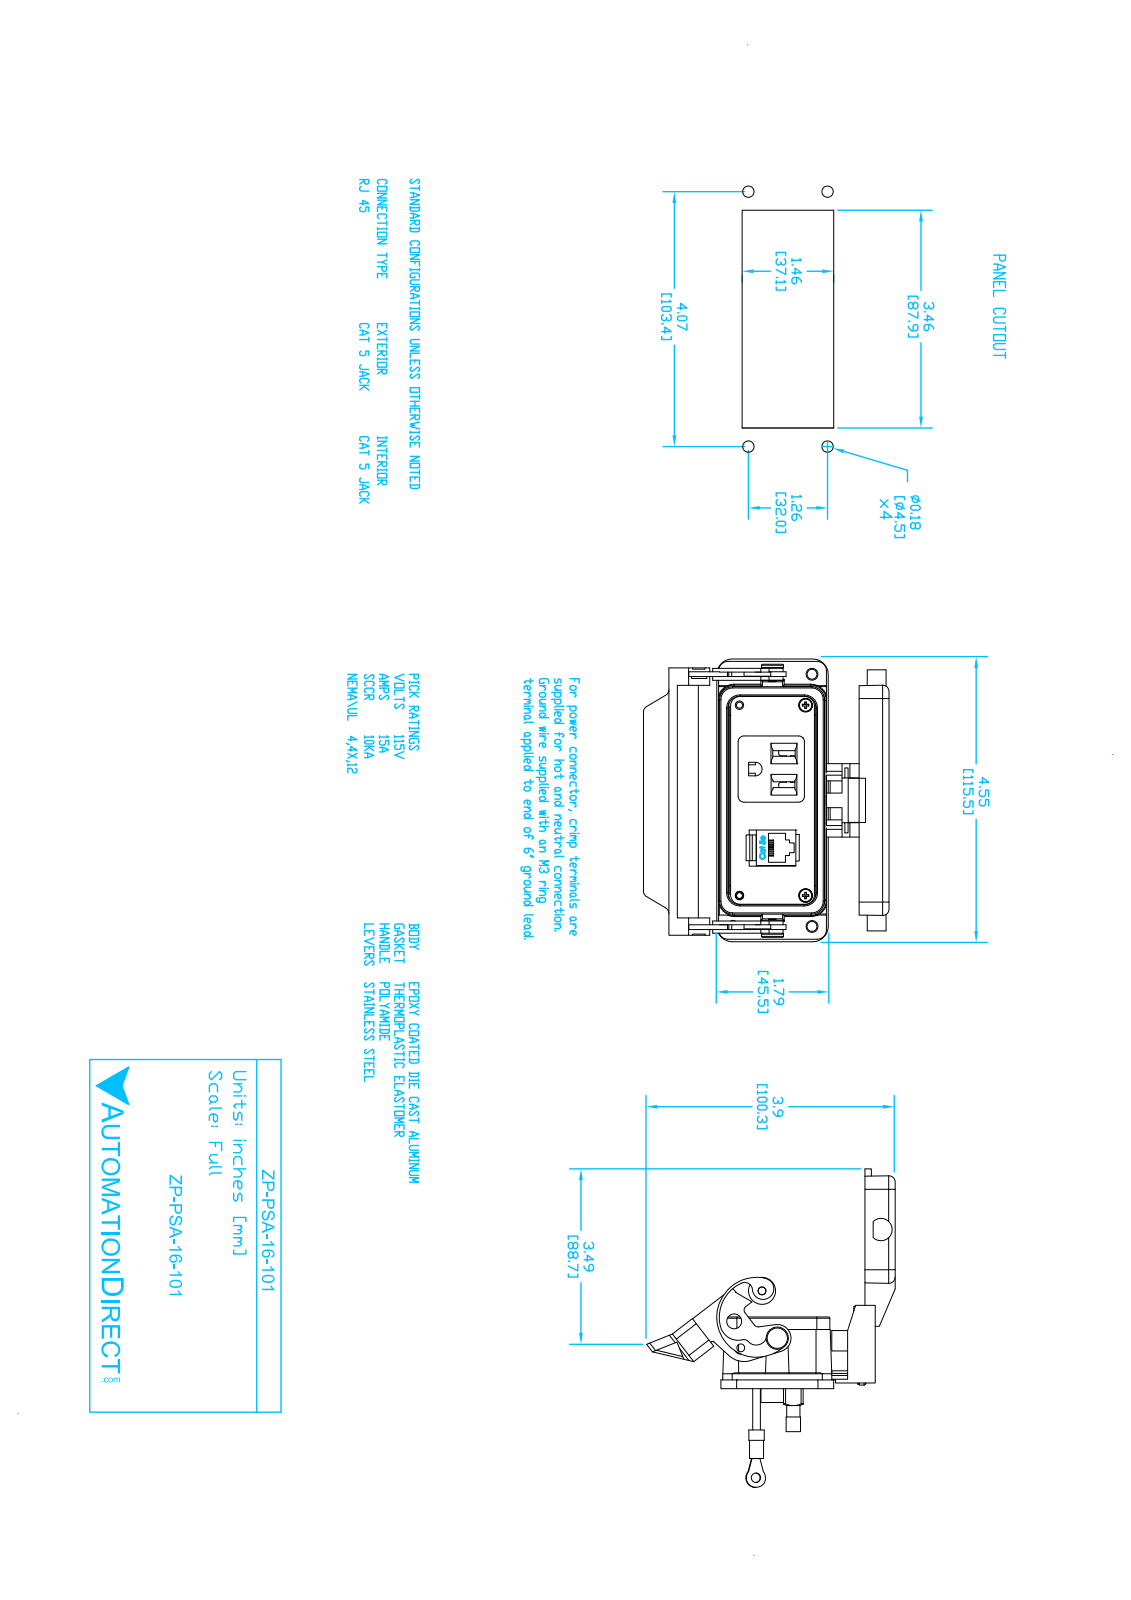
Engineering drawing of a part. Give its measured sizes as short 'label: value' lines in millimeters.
name: ZP-PSA-16-101
written by: SolidWorks 2017 (AUTOMOTIVE_DESIGN)
unit: mm
bodies: 1 solid, 1606 faces (981 planar, 386 cylindrical, 239 other)
size: 128.6 × 115.5 × 100.8
volume: 102 300 mm³; area: 68 450 mm²
holes: 6× ⌀4.1, 4× ⌀2.5, 4× ⌀3.7, 4× ⌀4.8, 2× ⌀3, 2× ⌀3.8, 2× ⌀5.1, 1× ⌀1.9, 1× ⌀2.2, 1× ⌀3.2, 1× ⌀3.3, 1× ⌀4
bosses: 4× ⌀5.7, 4× ⌀5.6, 4× ⌀3, 2× ⌀5.8, 2× ⌀5.3, 2× ⌀2.5, 1× ⌀10.9, 1× ⌀9
rounds: 16× R2.5, 13× R3.8, 12× R0.8, 10× R0.5, 9× R0.4, 8× R0.6, 8× R2.4, 8× R6.4
face distances: 1.5, 17.1, 18.6, 3.4, 2.9, 0.5, 103.3, 39.2, 40.7, 40.8
hole spacings: 12.8, 32, 90.5, 95.2, 27, 32, 78, 82.6
